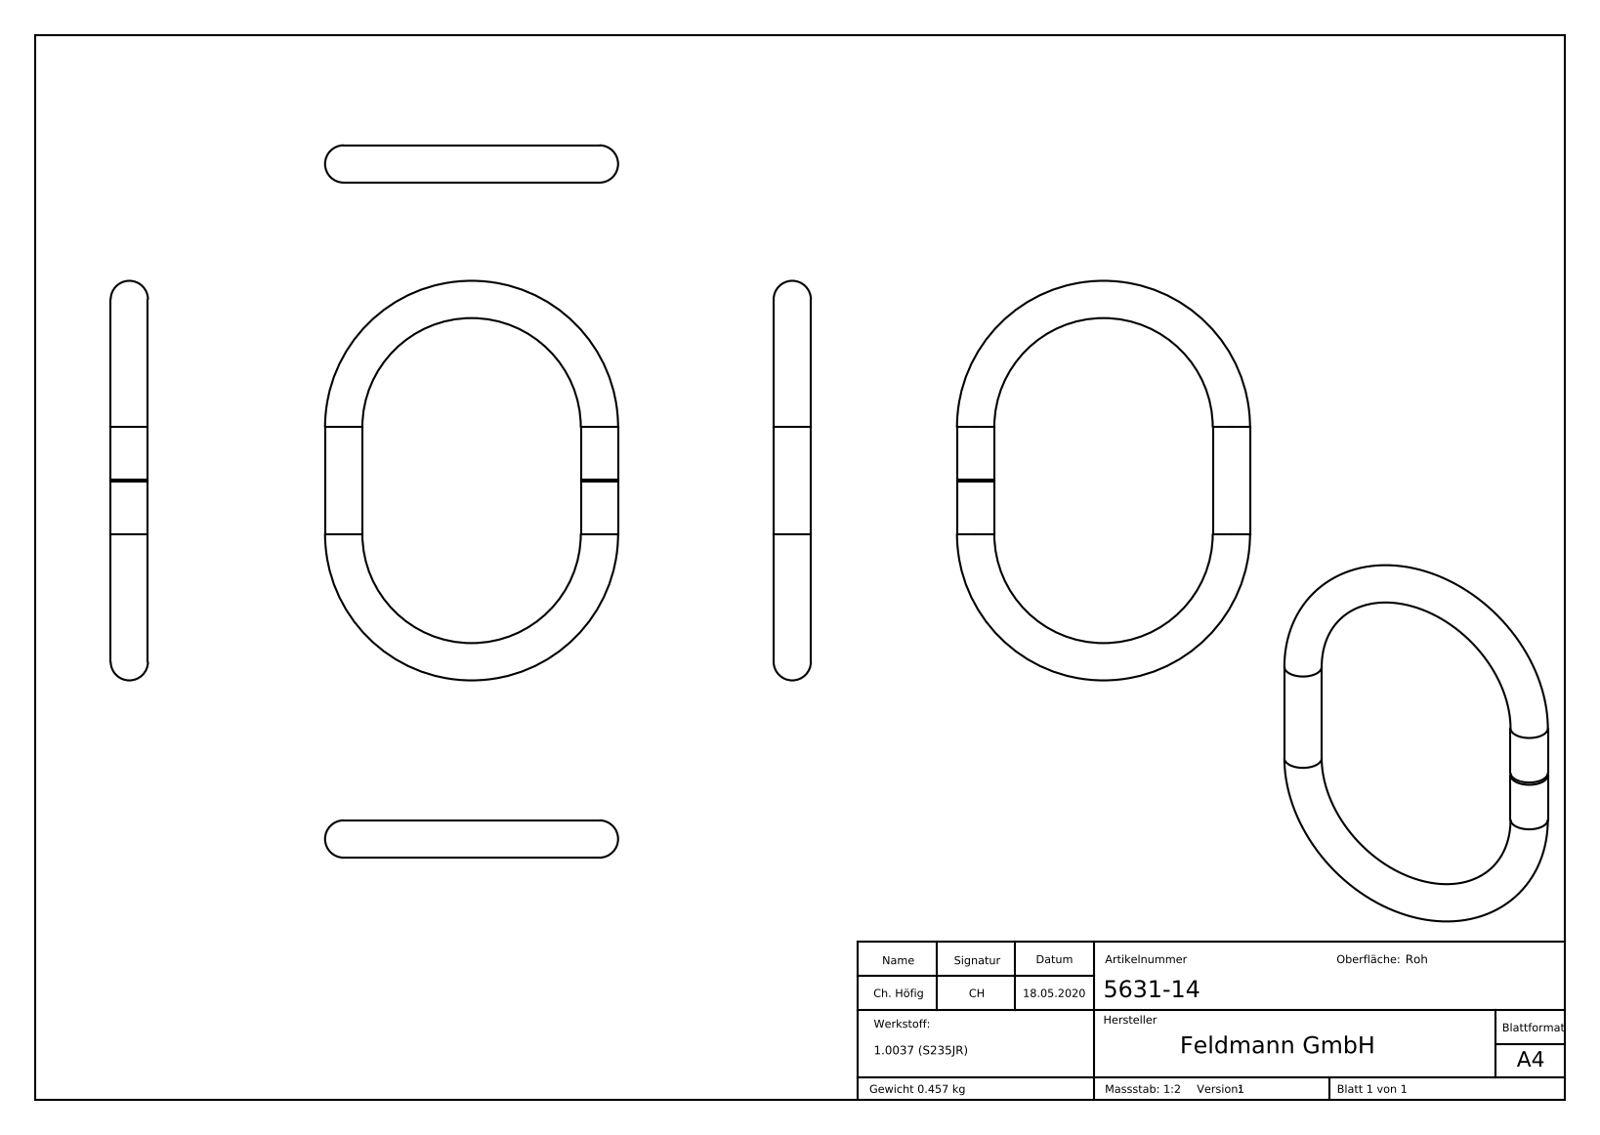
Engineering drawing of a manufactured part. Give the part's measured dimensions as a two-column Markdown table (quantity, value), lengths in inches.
| quantity | value |
| --- | --- |
| part name | 5631-14 |
| STEP written by | SolidWorks 2015 (CONFIG_CONTROL_DESIGN) |
| units | inches |
| bodies | 1 solid, 201 faces (117 planar, 3 cylindrical, 81 other) |
| overall size | 5.906 × 4.331 × 0.551 |
| volume | 3.575 in³ |
| surface area | 26.43 in² |
| round bosses / shafts (diameter × count) | 0.551 × 2 |
| main face-to-face distances | 0.039, 0.043, 0.07, 0.033, 0.021, 0.029, 0.013, 0.105, 0.078, 0.057 |
